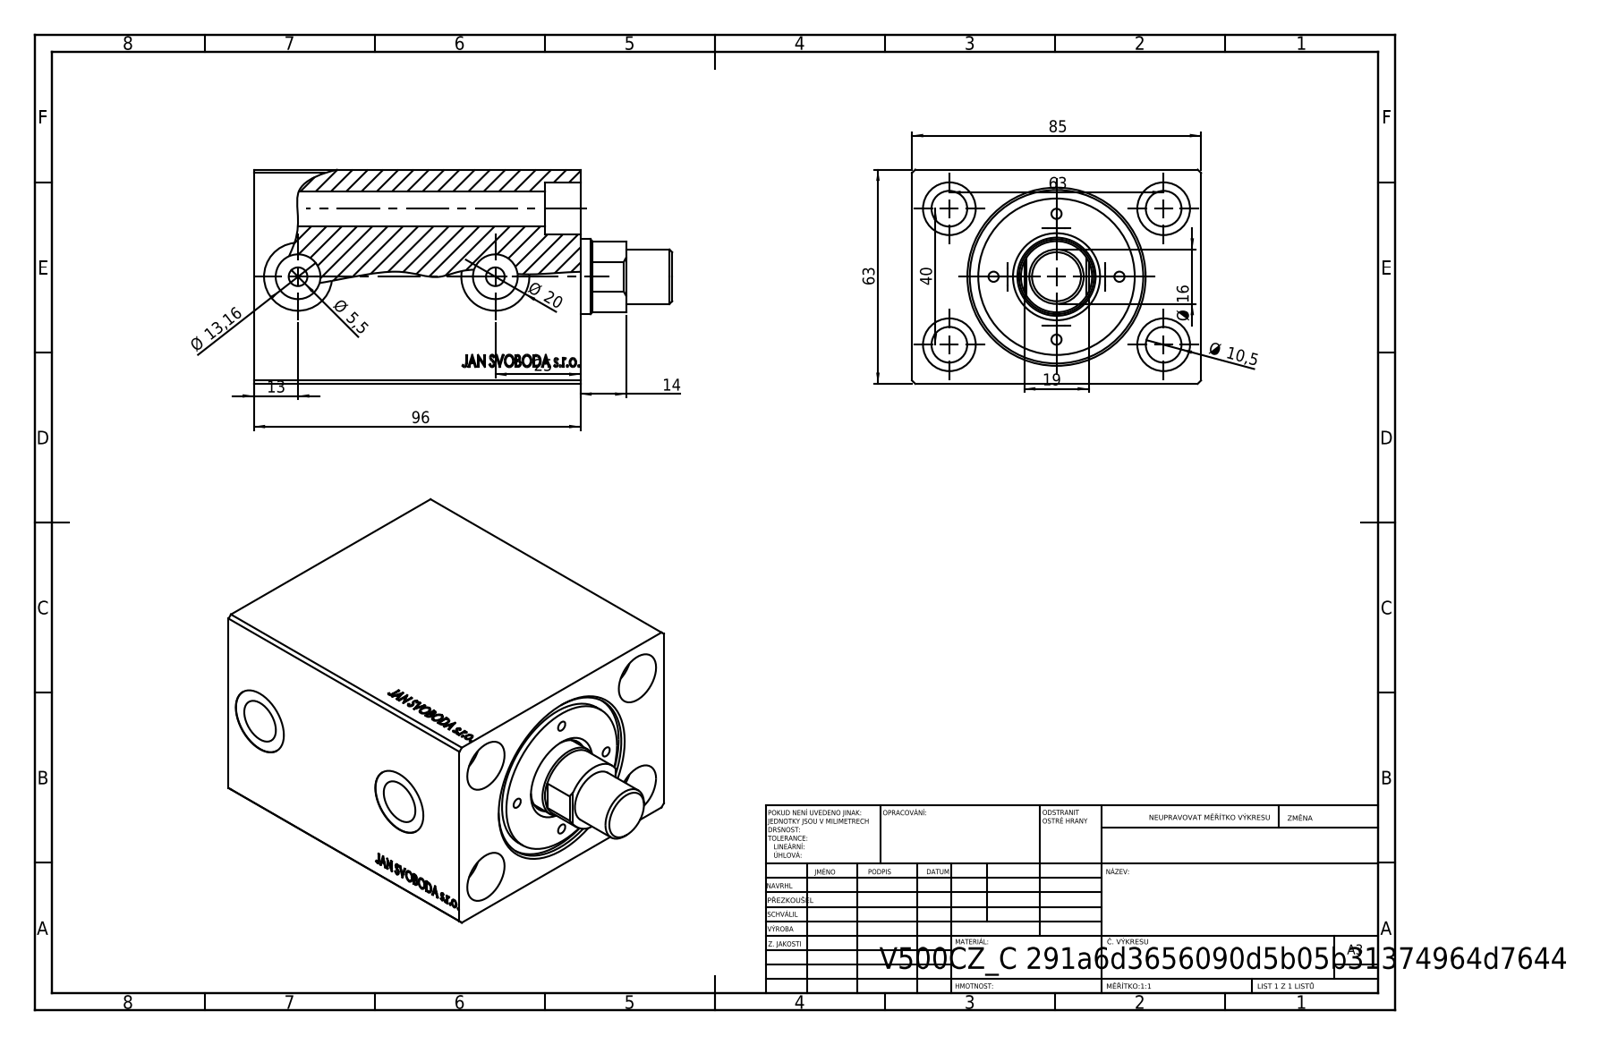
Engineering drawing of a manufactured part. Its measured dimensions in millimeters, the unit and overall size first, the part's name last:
Units: millimetres
Overall size (bounding box): 123 × 85 × 63
Round holes (diameter × count): ⌀3 ×4, ⌀10.5 ×4, ⌀15.5 ×4, ⌀5.5 ×2, ⌀13.16 ×2, ⌀20 ×2, ⌀16 ×1, ⌀22 ×1, ⌀23 ×1, ⌀36 ×1, ⌀40 ×1, ⌀51 ×1
Round bosses / shafts (diameter × count): ⌀46 ×1, ⌀14 ×1
Partial cylindrical surfaces — rounded edges, fillets, slot ends (radius × count): R10.46 ×1
Main face-to-face distances: 63, 85, 96, 60, 36, 25, 11.8, 48.2, 84.2, 10
Hole centre spacings: 18.5, 23.85, 26.16, 31.54, 37.31, 49.74, 53.85, 37
Volume: 453 377 mm³ · Surface area: 79 366 mm²
Bodies: 4 solids, 884 faces (413 planar, 71 cylindrical, 400 other)
Part name (STEP PRODUCT): V500CZ_VC_vysunovaci_C; V500CZ_MALE_METRIC; V500CZ_VCP_C; V500CZ_C
STEP written by: SolidWorks 2019 (CONFIG_CONTROL_DESIGN)
